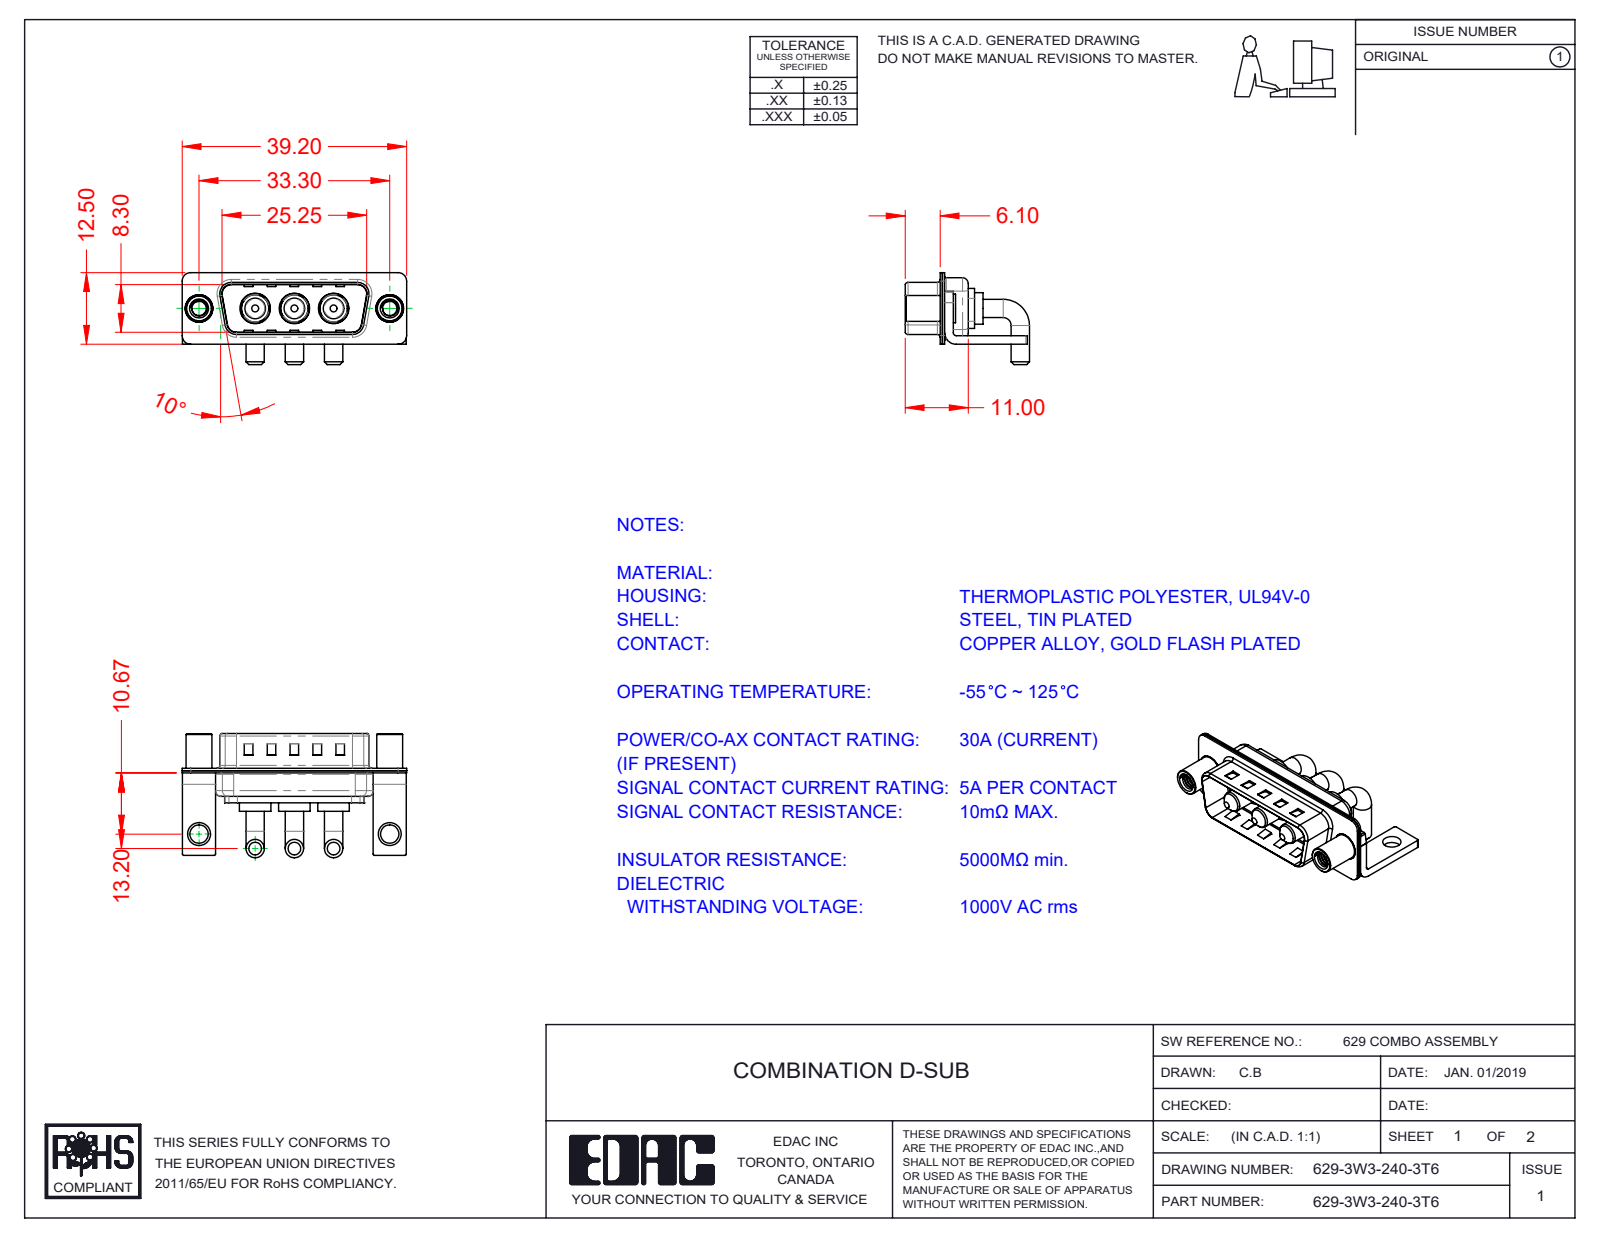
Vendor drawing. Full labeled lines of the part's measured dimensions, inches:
Part name (STEP PRODUCT): 629Combo Shell Front_15 Contacts; 629Combo Threaded Standoff_D; 629Combo Housing_3W3; 629Combo Stabilizer Bracket (+3 more)
STEP written by: SolidWorks 2020 (CONFIG_CONTROL_DESIGN)
Units: inches
Bodies: 13 solids, 567 faces (191 planar, 268 cylindrical, 108 other)
Overall size (bounding box): 1.543 × 0.854 × 0.632
Volume: 0.166 in³ · Surface area: 9.252 in²
Round holes (diameter × count): ⌀0.191 ×3, ⌀0.209 ×3, ⌀0.098 ×2, ⌀0.126 ×2, ⌀0.157 ×2, ⌀0.189 ×2
Round bosses / shafts (diameter × count): ⌀0.126 ×6, ⌀0.217 ×3, ⌀0.205 ×3, ⌀0.187 ×3, ⌀0.148 ×3, ⌀0.142 ×3, ⌀0.197 ×2, ⌀0.193 ×2
Partial cylindrical surfaces — rounded edges, fillets, slot ends (radius × count): R0.01 ×16, R0.059 ×16, R0.079 ×13, R0.02 ×9, R0.063 ×8, R0.024 ×4, R0.026 ×4, R0.035 ×4
Main face-to-face distances: 0.016, 0.031, 0.059, 0.374, 0.358, 0.343, 0.39, 0.205, 0.03, 0.024
Hole centre spacings: 0.27, 0.386, 0.656, 0.925, 1.311, 0.539
